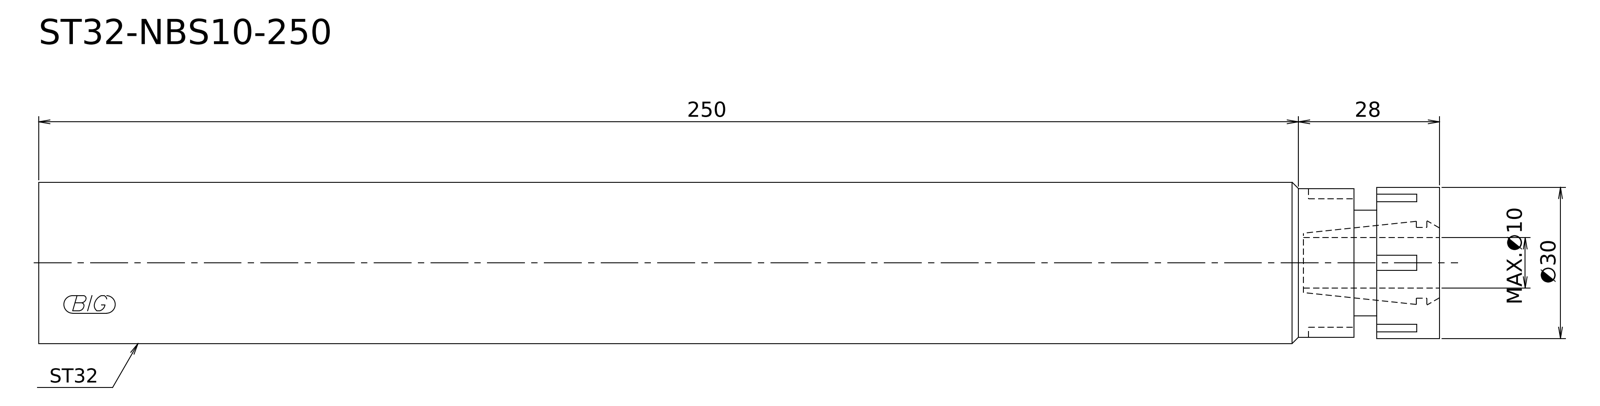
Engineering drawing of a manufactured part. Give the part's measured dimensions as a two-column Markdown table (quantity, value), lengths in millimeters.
| quantity | value |
| --- | --- |
| STEP written by | Kubotek KeyCreator V8.5.1 (14335) (CONFIG_CONTROL_DESIGN) |
| units | millimeters |
| bodies | 1 solid, 9 faces (4 planar, 4 cylindrical, 1 other) |
| overall size | 278 × 32 × 32 |
| volume | 218 898 mm³ |
| surface area | 29 881 mm² |
| round bosses / shafts (diameter × count) | 32 × 1, 30 × 1, 29.5 × 1, 21 × 1 |
| main face-to-face distances | 278, 12.5, 265.5, 17, 4.5, 261 |
